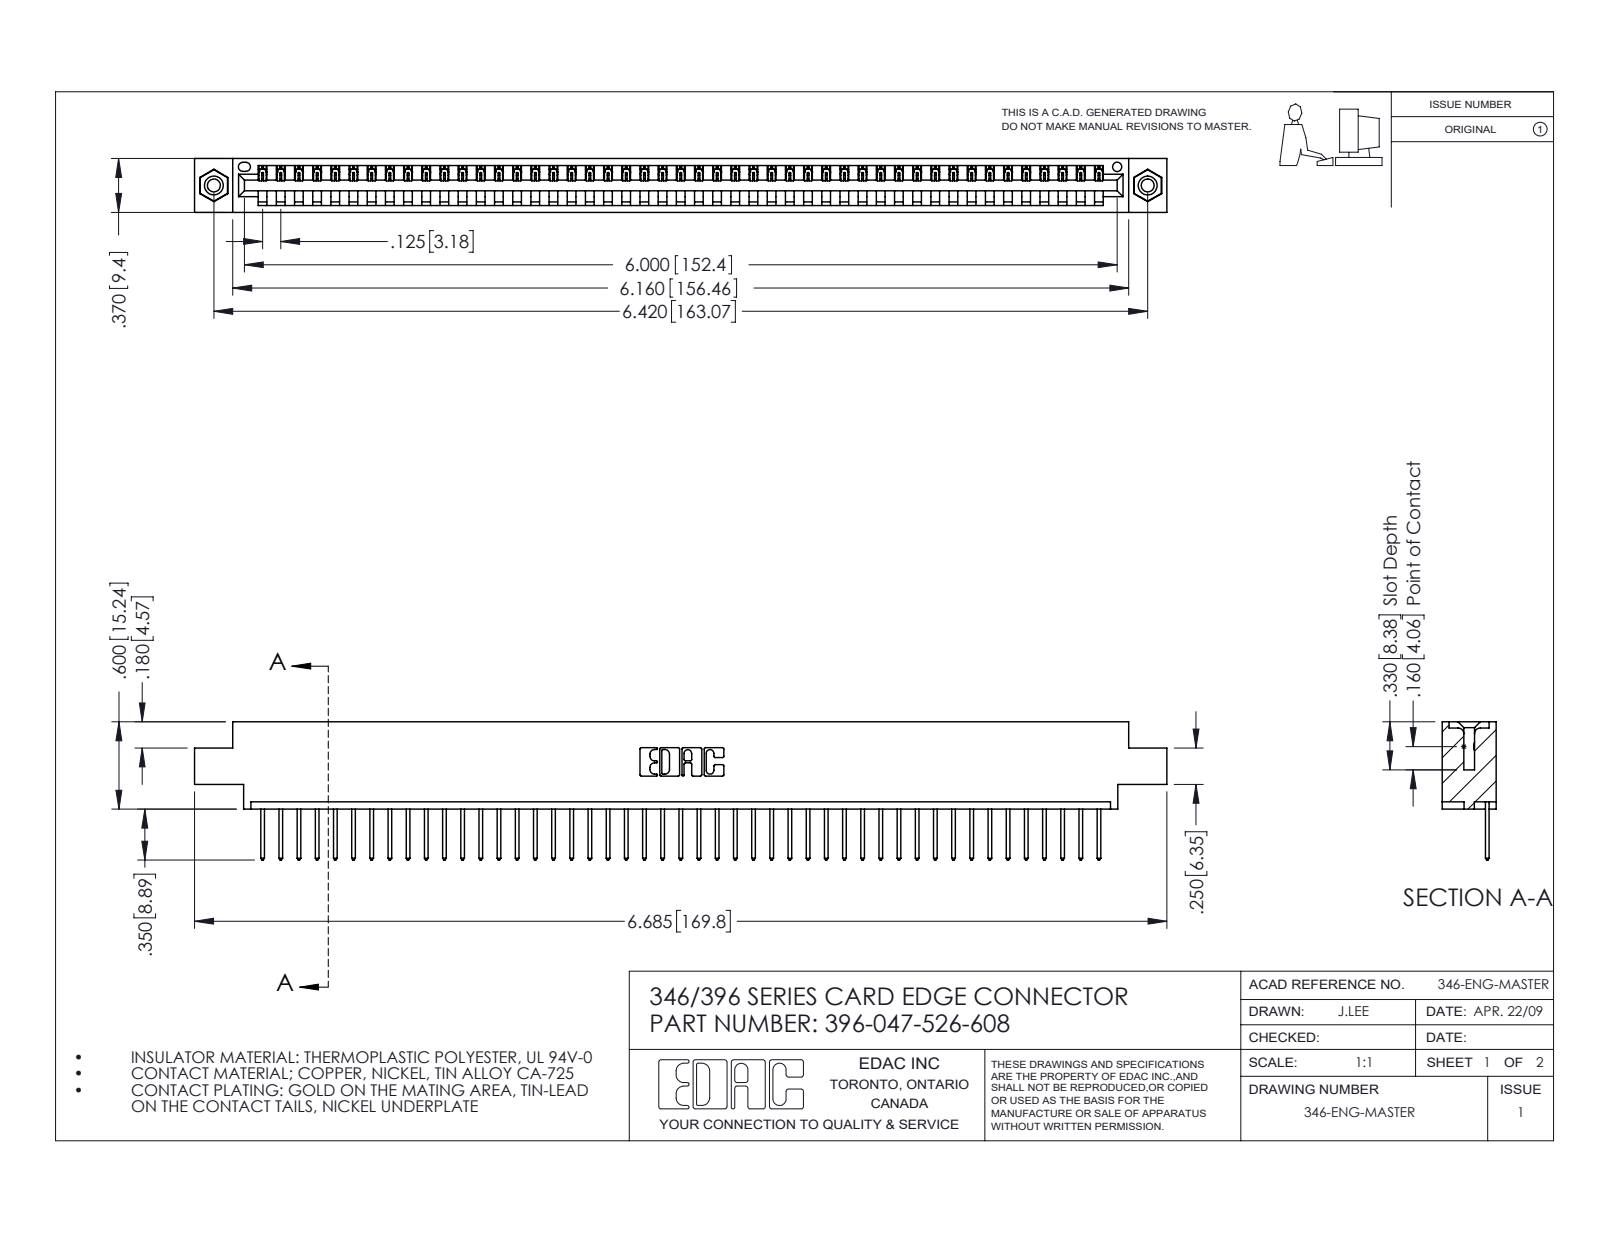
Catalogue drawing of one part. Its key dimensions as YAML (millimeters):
part_name: "346 Part_0.170 Offset - 0.156 Dia-TI; 396-047-526-608; 345-292-001_345-293-126; 345-250-001_345-250-003-102"
step_written_by: "SolidWorks 2016 (CONFIG_CONTROL_DESIGN)"
units: millimeters
bodies: {solids: 50, faces: 2912, planar: 1992, cylindrical: 904, other: 16}
overall_size: [169.8, 24.1, 9.4]
volume: 16100
surface_area: 20300
round_holes:
  - {diameter: 2.3, count: 2}
  - {diameter: 3.2, count: 2}
  - {diameter: 4, count: 2}
  - {diameter: 1.6, count: 1}
round_bosses_or_shafts:
  - {diameter: 3.9, count: 2}
partial_cylinders:
  - {radius: 0.2, count: 94}
  - {radius: 0.3, count: 94}
  - {radius: 0.3, count: 22}
  - {radius: 0.2, count: 6}
  - {radius: 0.8, count: 6}
  - {radius: 0.7, count: 3}
  - {radius: 0.8, count: 2}
  - {radius: 1, count: 2}
face_to_face_distances: [1.2, 8.2, 9.4, 6.4, 1.8, 7.6, 0.6, 5.6, 3.8, 2.5]
hole_center_spacings: [6.2, 157.8, 163.1]
